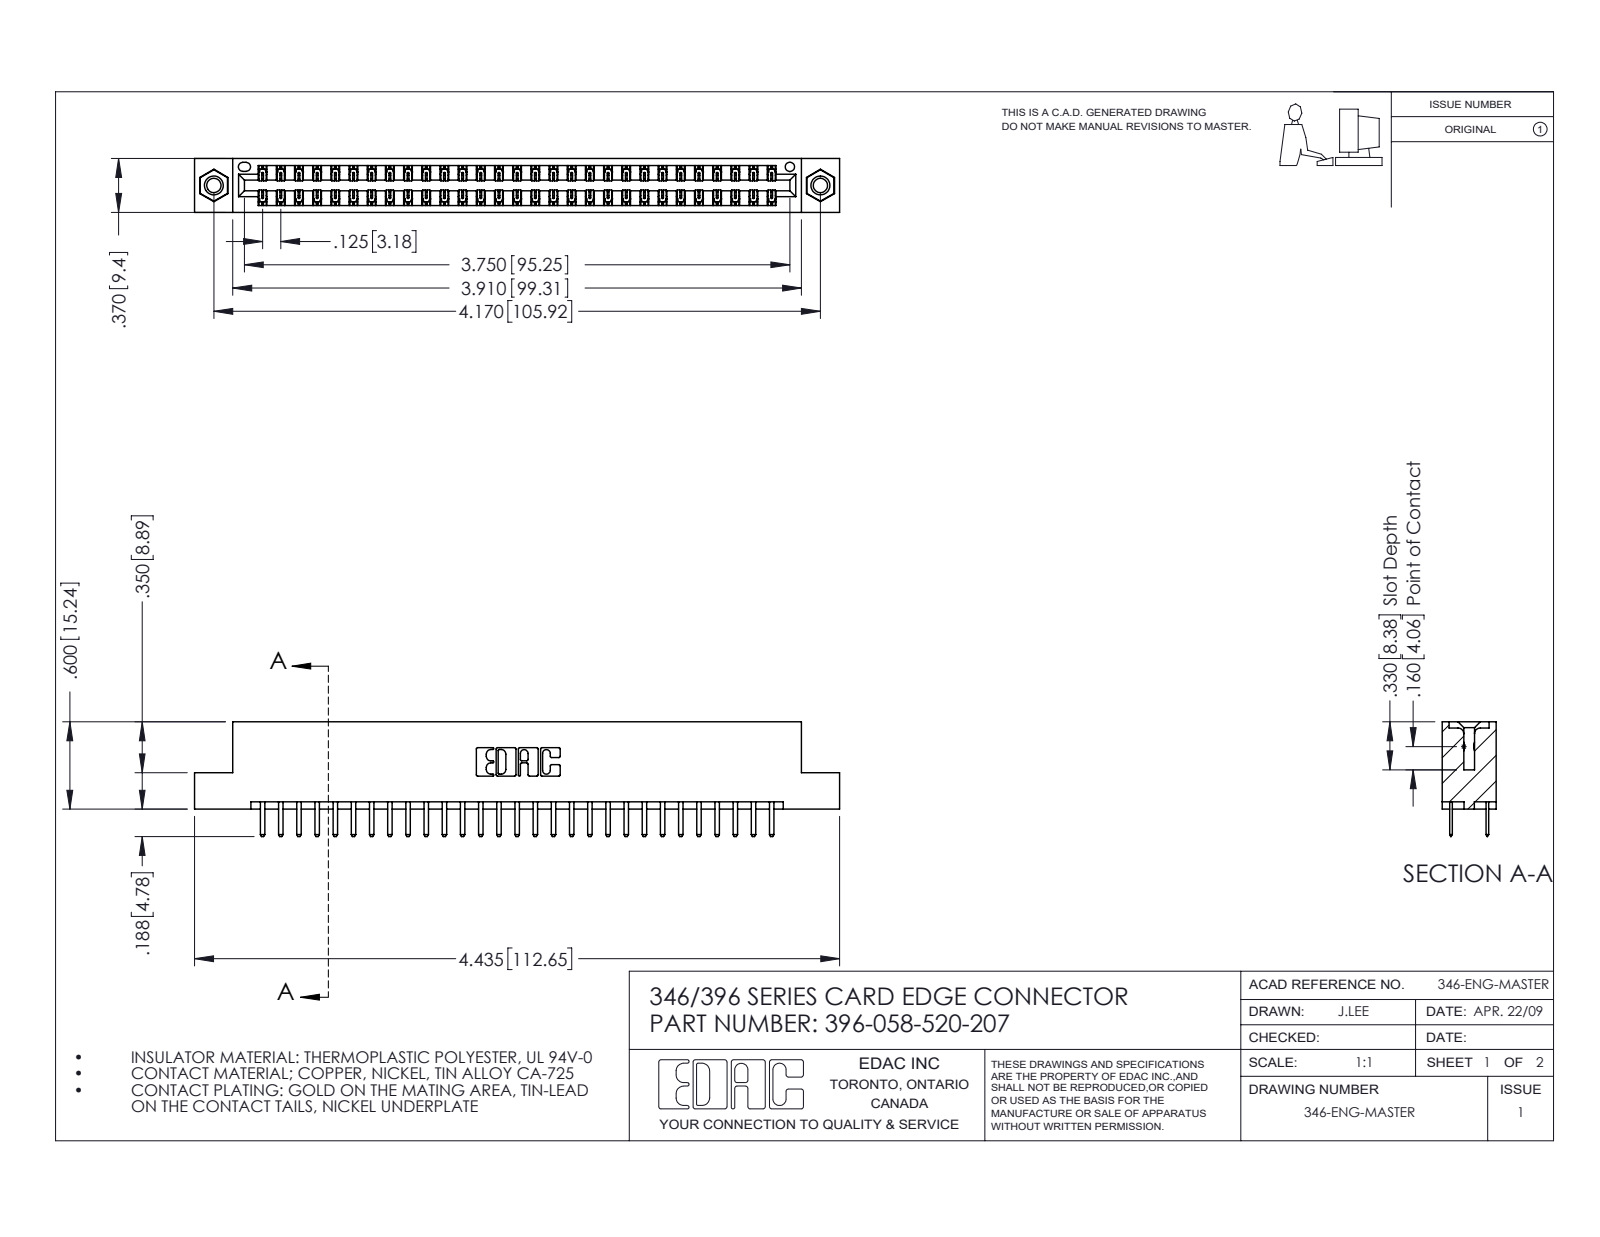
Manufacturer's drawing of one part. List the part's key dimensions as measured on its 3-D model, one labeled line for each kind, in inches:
Part name (STEP PRODUCT): 396-058-520-207; 346 Part_Flush Mounting Lugs - 0.156 Dia-TI; 345-250-001_345-250-005-103; 345-292-001_345-293-120
STEP written by: SolidWorks 2016 (CONFIG_CONTROL_DESIGN)
Units: inches
Bodies: 61 solids, 3430 faces (2254 planar, 1160 cylindrical, 16 other)
Overall size (bounding box): 4.435 × 0.788 × 0.37
Volume: 0.662 in³ · Surface area: 22.75 in²
Round holes (diameter × count): ⌀0.098 ×2, ⌀0.125 ×2, ⌀0.156 ×2, ⌀0.064 ×1
Round bosses / shafts (diameter × count): ⌀0.155 ×2
Partial cylindrical surfaces — rounded edges, fillets, slot ends (radius × count): R0.006 ×87, R0.01 ×62, R0.01 ×22, R0.007 ×6, R0.031 ×6, R0.026 ×3, R0.014 ×2, R0.022 ×2
Main face-to-face distances: 0.048, 0.322, 0.25, 0.37, 0.275, 0.072, 0.298, 0.025, 0.148, 0.222
Hole centre spacings: 0.246, 3.962, 4.17
